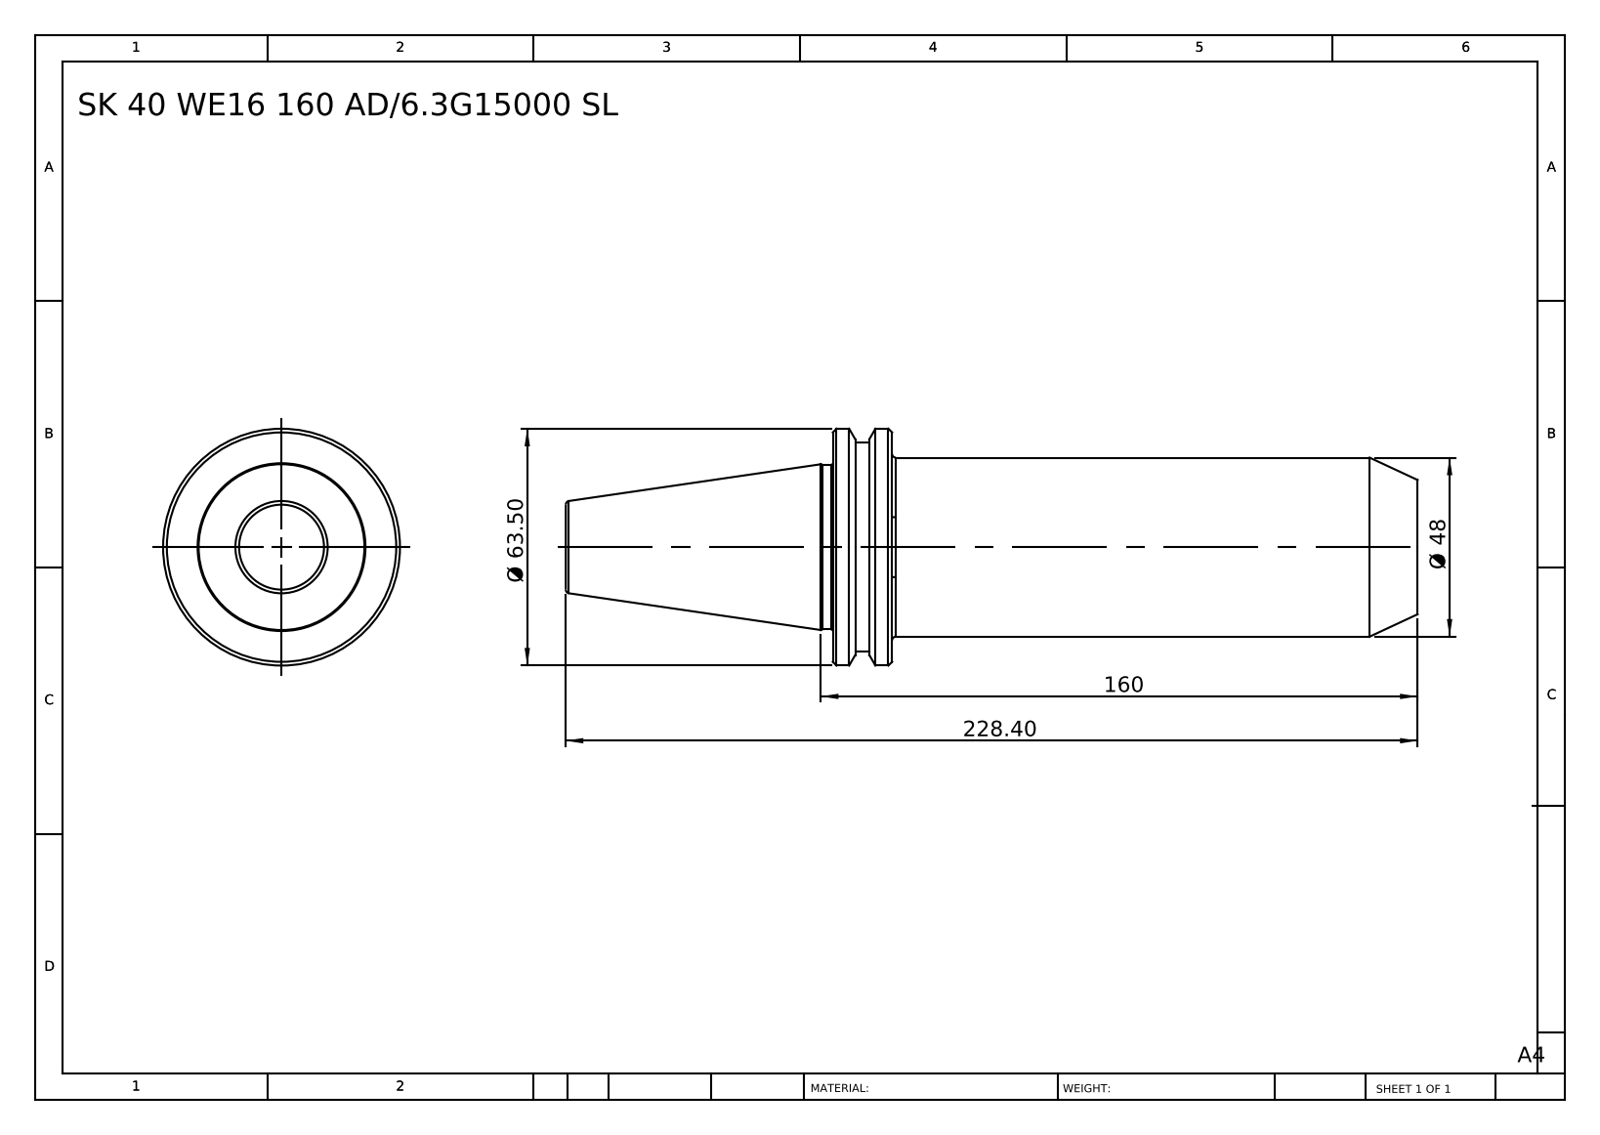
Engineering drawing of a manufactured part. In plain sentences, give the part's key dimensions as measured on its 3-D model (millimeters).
The part is named "SK40 WE16 160 AD-6.3G15000 SL". Its 3-D file was written by "SolidWorks 2014 (CONFIG_CONTROL_DESIGN)". It is 1 solid with 36 faces: 6 planar, 10 cylindrical and 20 other. Overall it measures 228.4 by 63.5 by 63.5 millimeters. Its volume is 366 769 cubic millimeters and its surface area 37 266 square millimeters. Round bosses or shafts: 1 of diameter 63.5, 1 of diameter 56, 1 of diameter 48, 1 of diameter 44. The main face-to-face distances are 156.8, 140.9, 15.9, 228.4, 87.5, 71.6, 147, 6.1, 9.8, 81.4.
